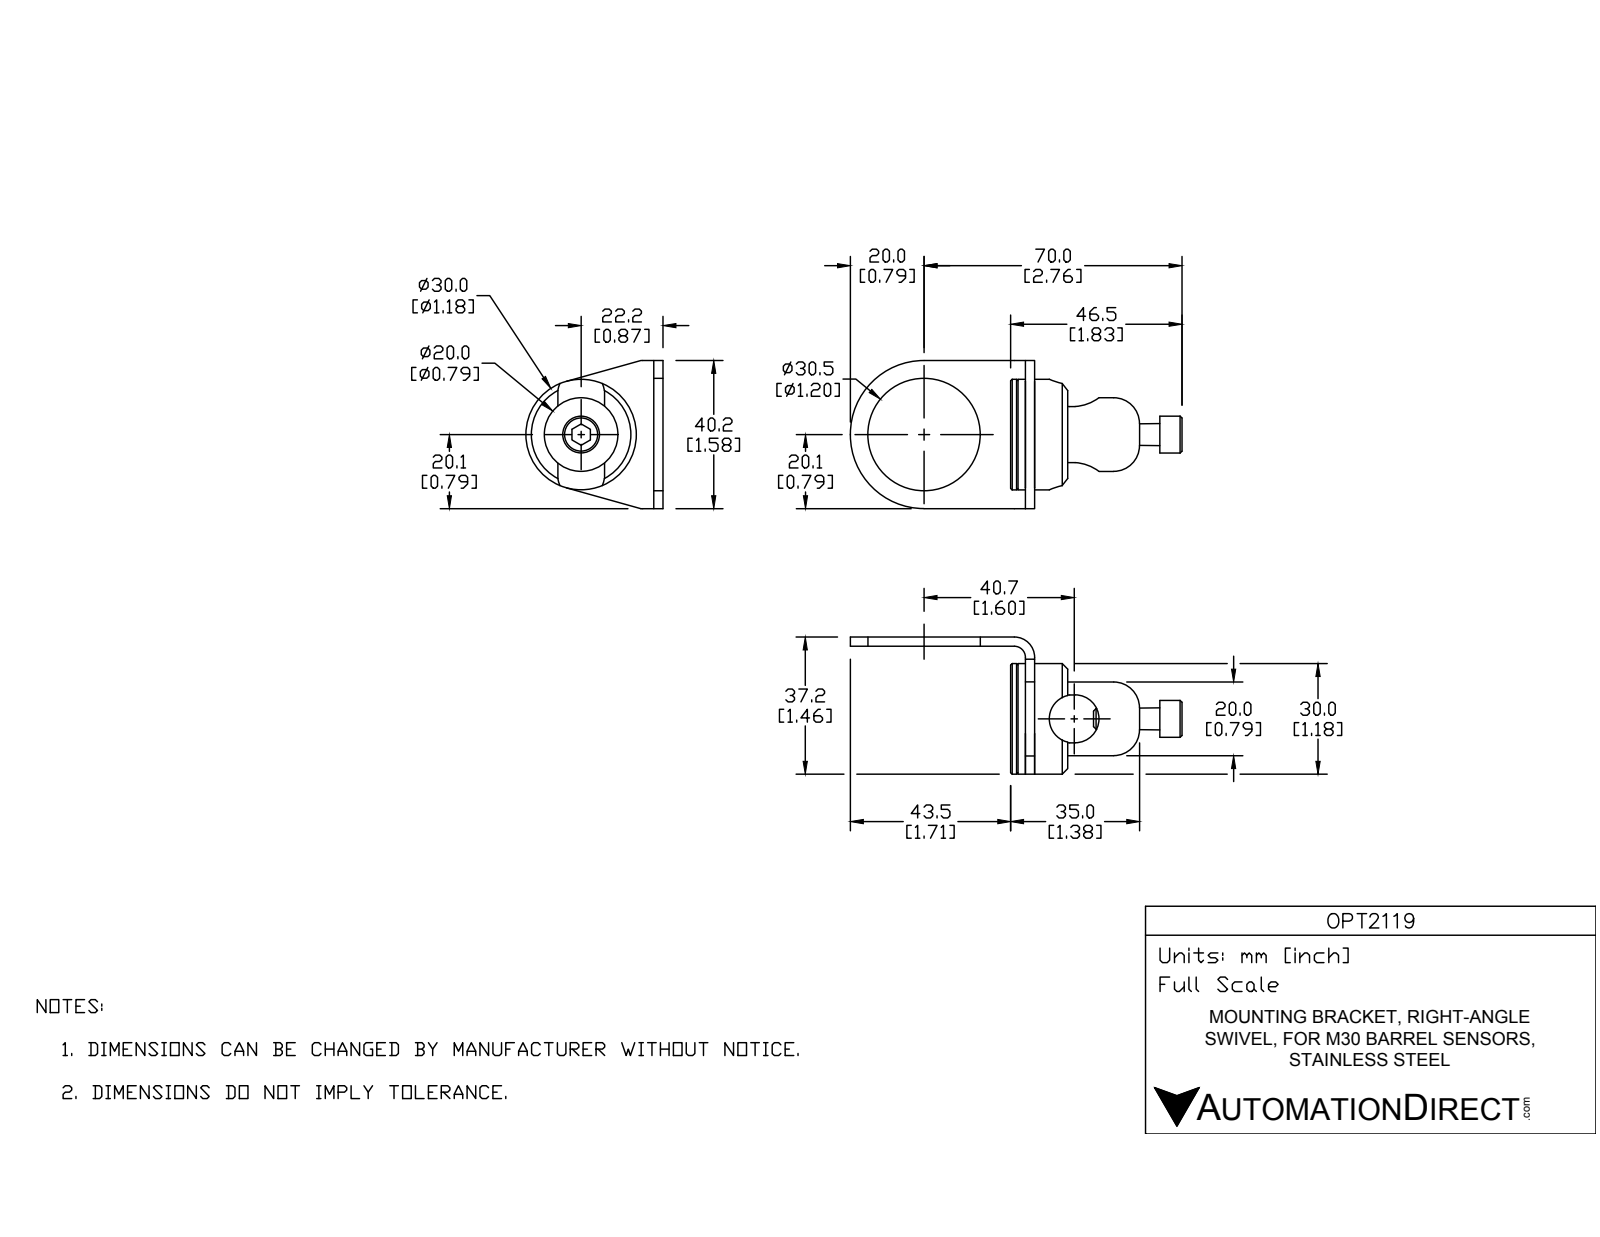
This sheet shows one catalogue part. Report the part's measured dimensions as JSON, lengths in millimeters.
{"step_written_by": "Unknown (CONFIG_CONTROL_DESIGN)", "units": "millimeters", "bodies": {"solids": 4, "faces": 116, "planar": 58, "cylindrical": 40, "other": 18}, "overall_size": [90, 70.1, 55.2], "volume_mm3": 34183, "surface_area_mm2": 20641, "round_holes": [[20.1, 2], [30.5, 2], [20, 1], [21, 1]], "round_bosses_or_shafts": [[30, 1], [10, 1]], "partial_cylinders_radius": [[20, 4], [6.5, 3], [3, 2], [5.5, 2], [15, 1]], "face_to_face_distances": [2.5, 4, 6.5, 1.5, 13, 9, 11.5, 15.5, 2, 20.1], "hole_center_spacings": [36.11]}
